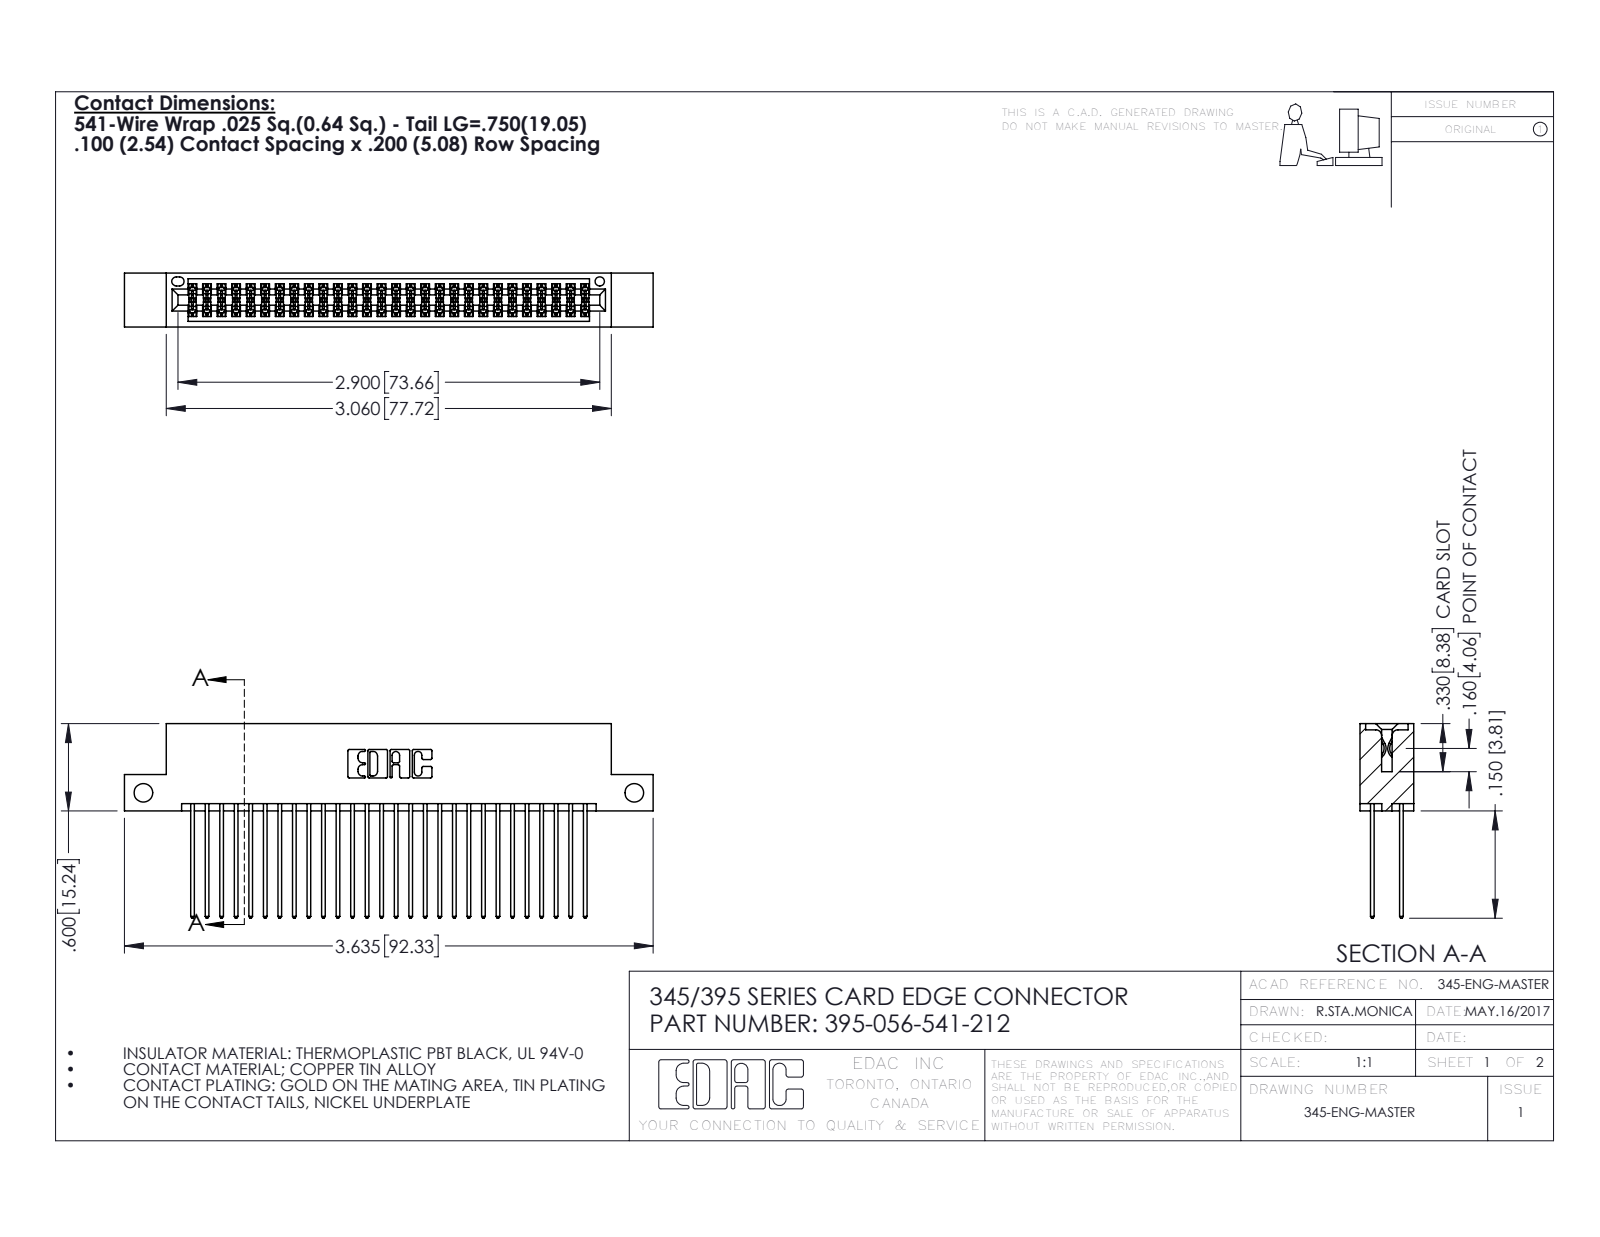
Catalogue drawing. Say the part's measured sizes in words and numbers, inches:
The part is named "345-292-001_345-293-141; 345 Part_Flush Mounting Lugs - Side Mount; 395-056-541-212". Its 3-D file was written by "SolidWorks 2016 (CONFIG_CONTROL_DESIGN)". It is 57 solids with 2926 faces: 1928 planar, 998 cylindrical and 0 other. Overall it measures 3.635 by 1.337 by 0.37 inches. Its volume is 0.554 cubic inches and its surface area 22.5 square inches. Round holes: 2 of diameter 0.128, 1 of diameter 0.064. Partial cylindrical surfaces (rounded edges, fillets, slot ends): 84 of radius 0.006, 56 of radius 0.01, 22 of radius 0.01, 6 of radius 0.007, 6 of radius 0.031, 3 of radius 0.026, 2 of radius 0.014, 2 of radius 0.019. The main face-to-face distances are 0.298, 0.072, 0.2, 0.098, 0.272, 0.025, 0.225, 0.37, 0.175, 0.149. The hole center spacings are 3.375.
